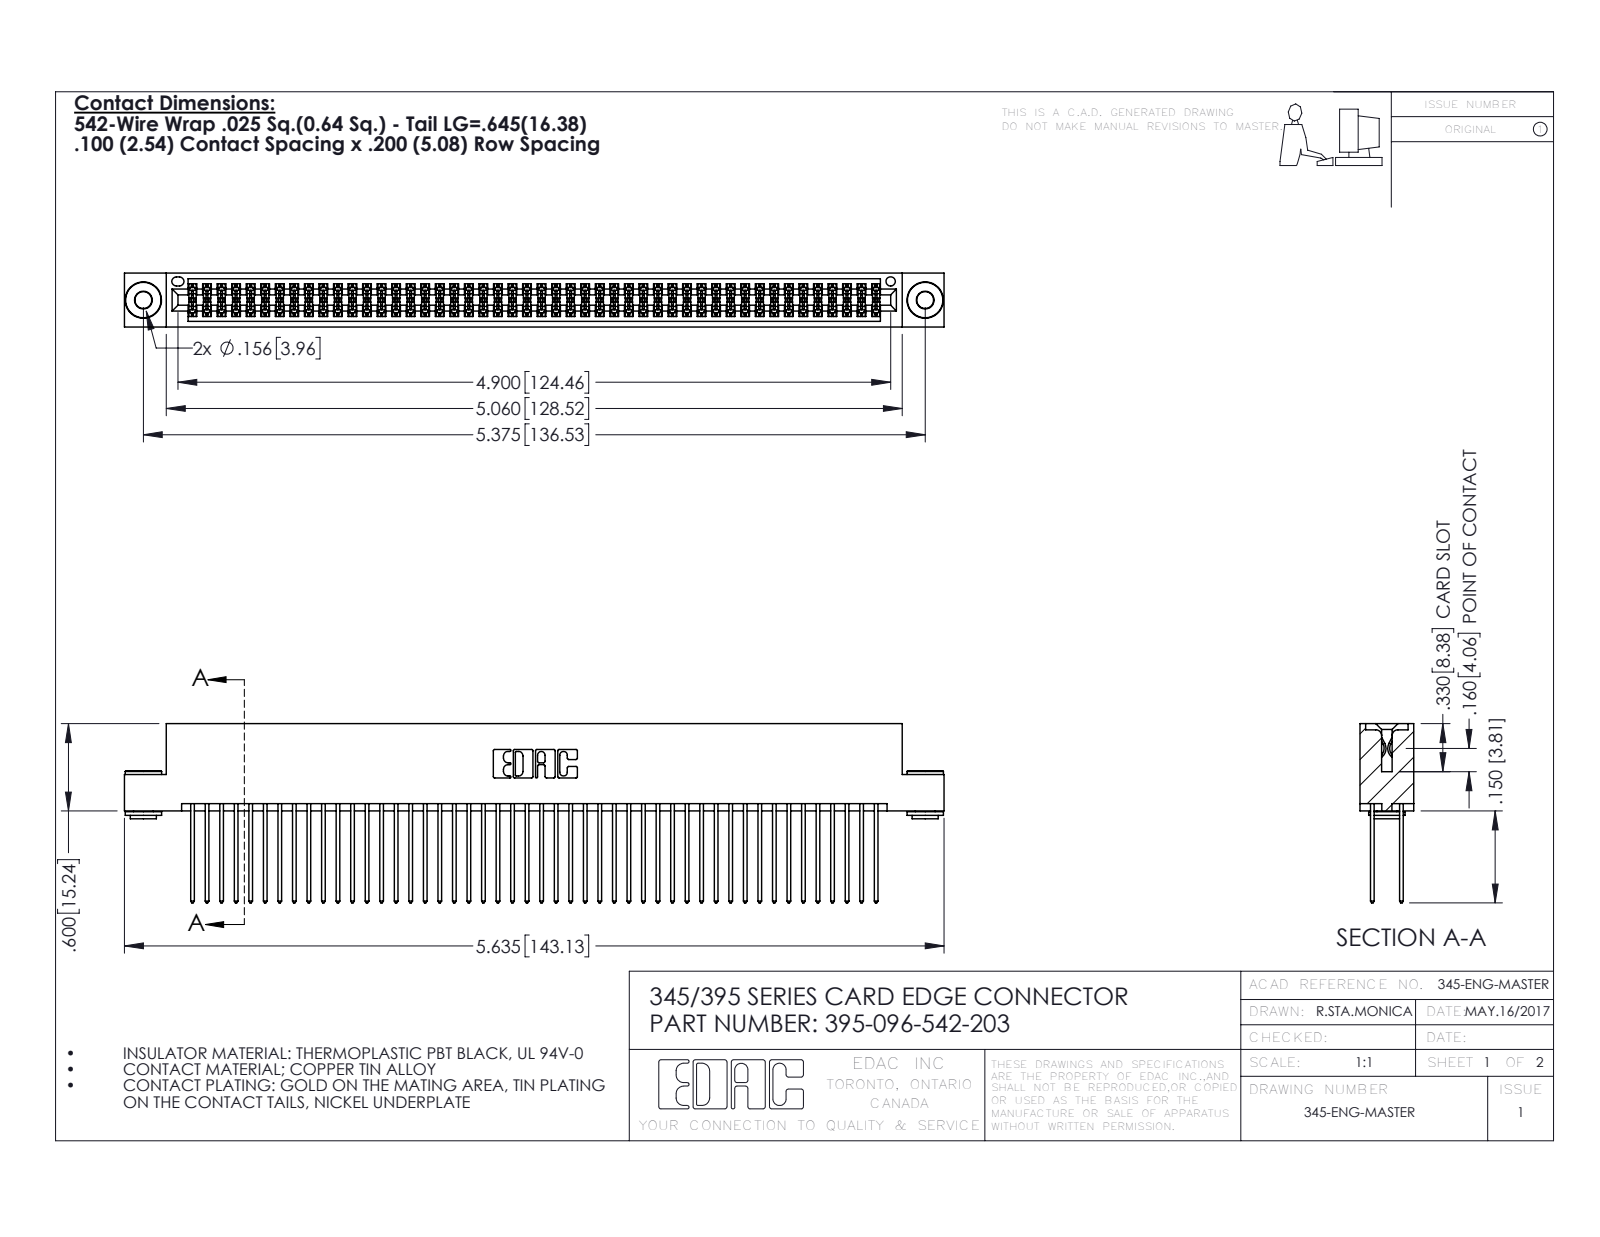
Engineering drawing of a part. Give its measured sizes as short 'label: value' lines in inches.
name: 345 Part_Flush Mounting Lugs - 0.156 Dia-TH; 345-292-001_345-293-142; 345-250-002_345-250-002-102; 395-096-542-203
written by: SolidWorks 2016 (CONFIG_CONTROL_DESIGN)
unit: in
bodies: 99 solids, 4964 faces (3258 planar, 1698 cylindrical, 8 other)
size: 5.635 × 1.232 × 0.37
volume: 0.88 in³; area: 36.79 in²
holes: 2× ⌀0.116, 2× ⌀0.156, 1× ⌀0.064
bosses: 2× ⌀0.25, 2× ⌀0.18, 2× ⌀0.136
rounds: 144× R0.006, 96× R0.01, 22× R0.01, 6× R0.007, 6× R0.031, 3× R0.026, 2× R0.014, 2× R0.019
face distances: 0.072, 0.298, 0.2, 0.025, 0.098, 0.272, 0.225, 0.37, 0.175, 0.149
hole spacings: 0.27, 5.139, 5.375
